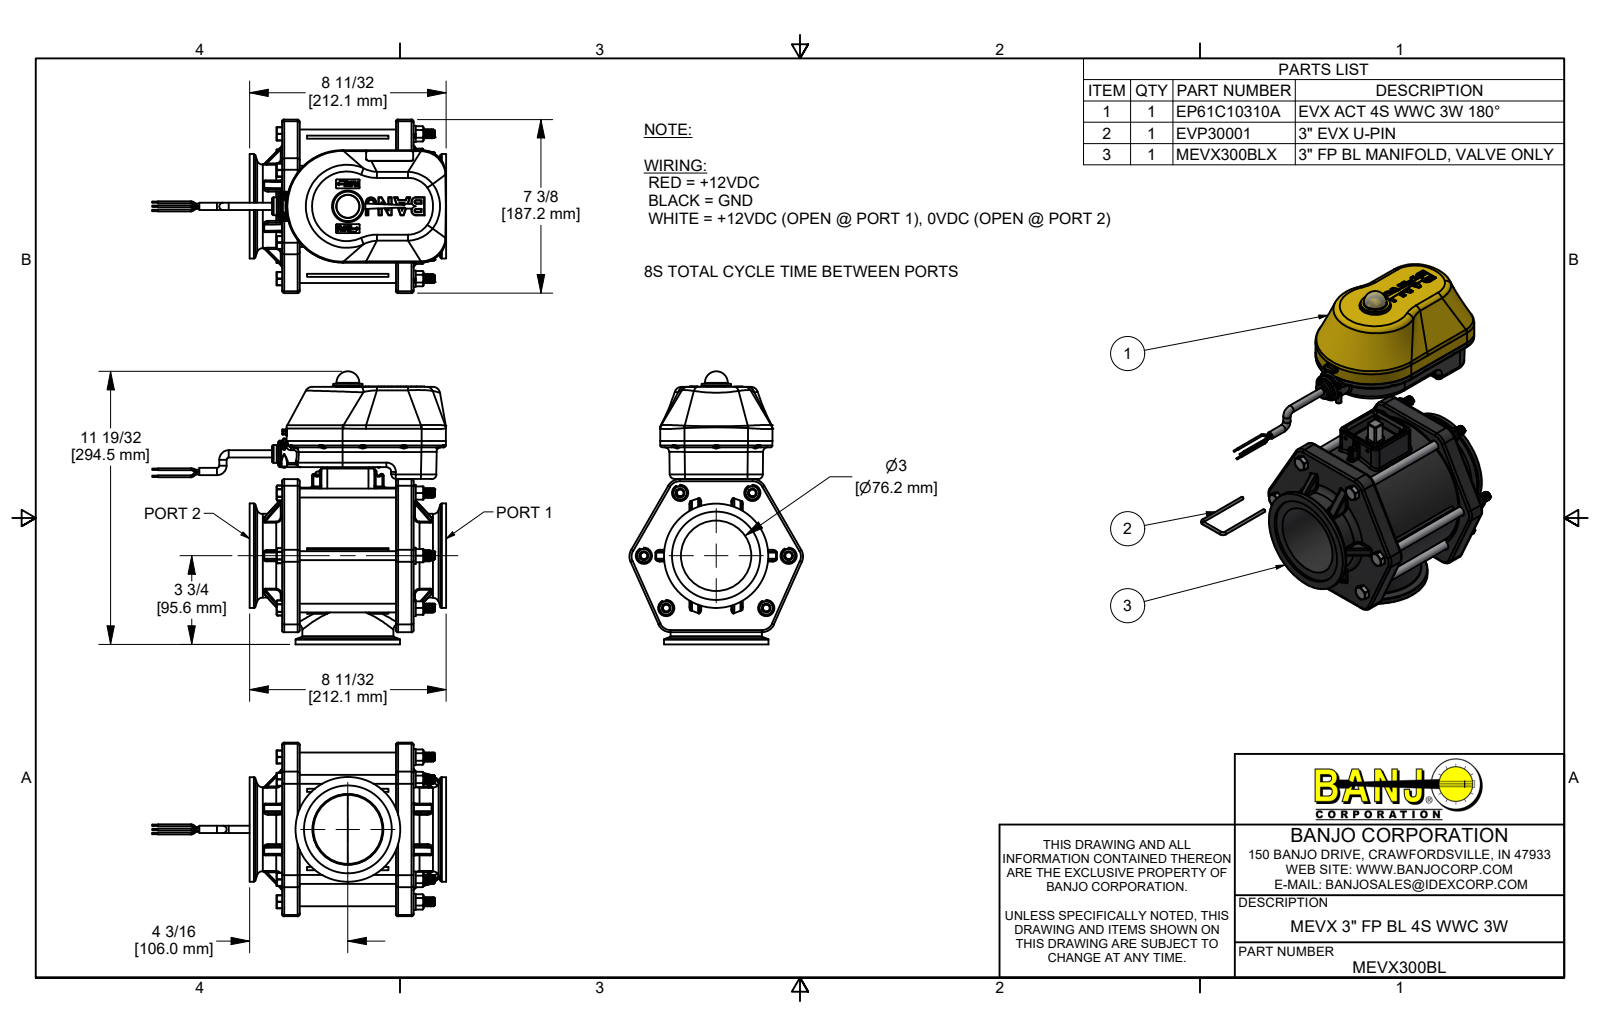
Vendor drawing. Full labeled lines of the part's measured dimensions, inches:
Part name (STEP PRODUCT): MEVX300BL; MEVX300BLX; MEVX35254BL; MEVX35254BLX (+8 more)
STEP written by: Autodesk Inventor 2022 (AUTOMOTIVE_DESIGN)
Units: inches
Bodies: 97 solids, 8994 faces (3069 planar, 3606 cylindrical, 2319 other)
Overall size (bounding box): 12.486 × 11.594 × 7.37
Volume: 168.5 in³ · Surface area: 1 196 in²
Round holes (diameter × count): ⌀0.15 ×15, ⌀0.095 ×11, ⌀0.34 ×11, ⌀0.44 ×8, ⌀0.08 ×7, ⌀0.307 ×6, ⌀0.385 ×6, ⌀0.104 ×4, ⌀0.136 ×4, ⌀0.148 ×4, ⌀0.176 ×4, ⌀0.266 ×4
Round bosses / shafts (diameter × count): ⌀0.25 ×19, ⌀0.08 ×15, ⌀0.375 ×11, ⌀0.14 ×11, ⌀0.108 ×11, ⌀0.085 ×11, ⌀0.687 ×6, ⌀0.294 ×6
Partial cylindrical surfaces — rounded edges, fillets, slot ends (radius × count): R0.013 ×204, R0.405 ×138, R0.387 ×114, R0.309 ×112, R0.01 ×111, R0.253 ×108, R0.609 ×106, R0.06 ×58
Main face-to-face distances: 0.69, 4.9, 0.5, 0.215, 5.59, 0.06, 0.905, 4.685, 3.995, 0.083
Hole centre spacings: 3.075, 2.417, 3.075, 5.917, 4.263, 2.272, 3.571, 4.92
